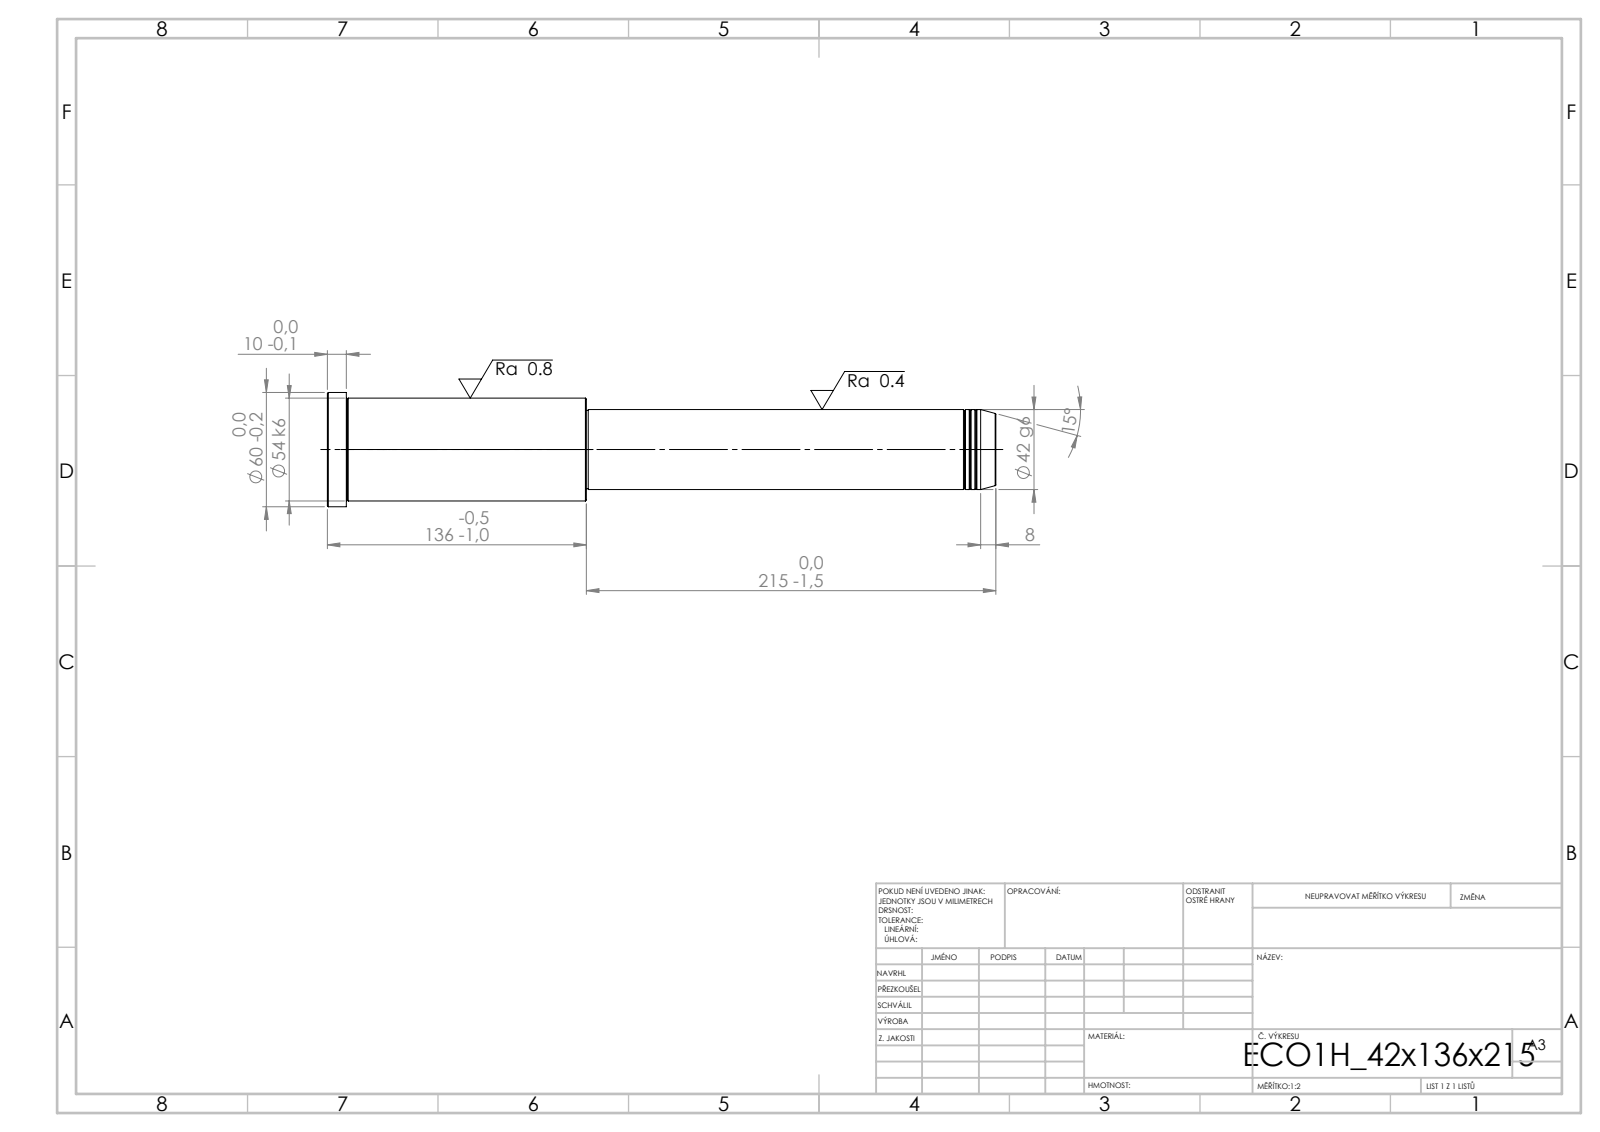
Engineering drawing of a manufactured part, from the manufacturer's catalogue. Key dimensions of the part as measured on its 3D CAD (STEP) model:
STEP written by: SolidWorks 2019 (CONFIG_CONTROL_DESIGN)
Units: millimetres
Bodies: 1 solid, 43 faces (5 planar, 14 cylindrical, 24 other)
Overall size (bounding box): 351 × 60 × 60
Volume: 613 286 mm³ · Surface area: 57 315 mm²
Round bosses / shafts (diameter × count): ⌀60 ×1, ⌀54 ×1, ⌀42 ×1, ⌀41 ×1
Main face-to-face distances: 351, 215, 136, 341, 126, 10, 214, 1, 127, 137
